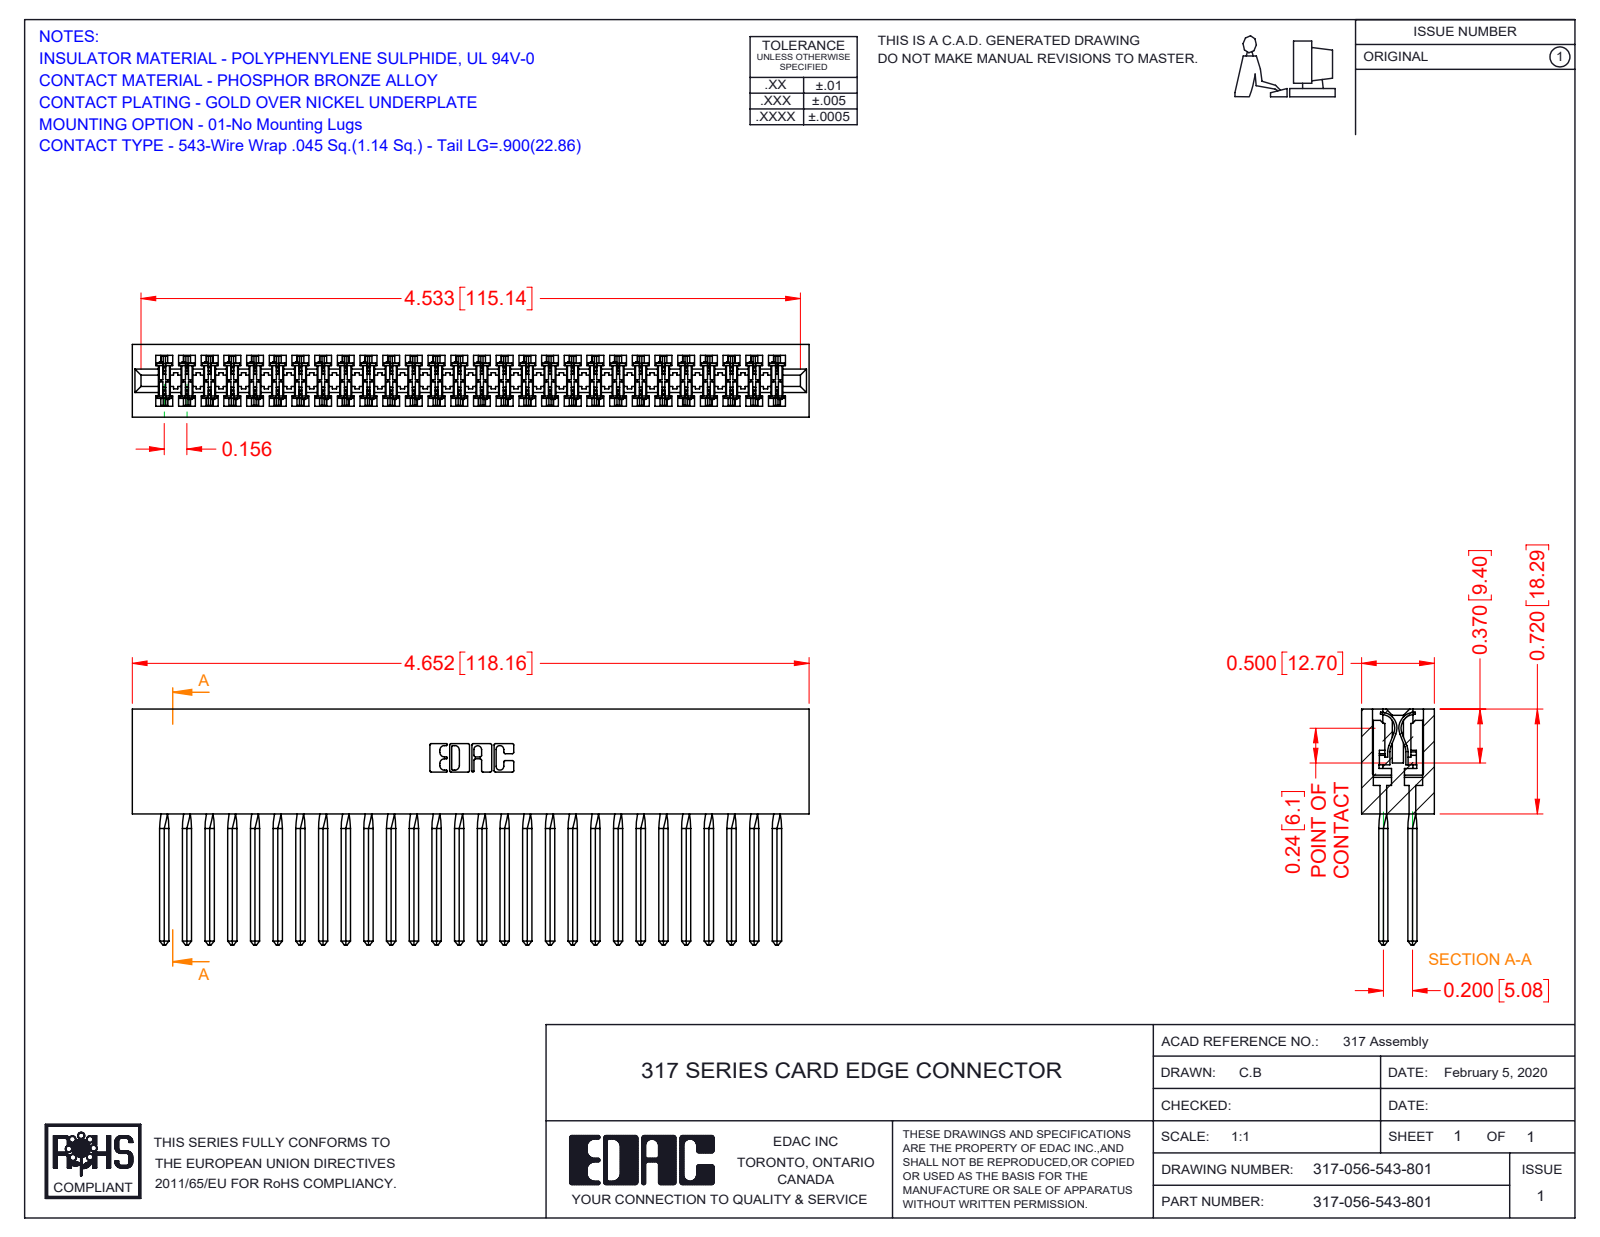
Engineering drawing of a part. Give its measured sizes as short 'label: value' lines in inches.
name: 317-056-543-801; 317 Part_Lugless; 317-290-001_543
written by: SolidWorks 2016 (CONFIG_CONTROL_DESIGN)
unit: in
bodies: 57 solids, 5074 faces (4138 planar, 712 cylindrical, 224 other)
size: 4.652 × 1.62 × 0.5
volume: 1.308 in³; area: 49.97 in²
rounds: 112× R0.015, 22× R0.01, 6× R0.007, 6× R0.031, 3× R0.026, 2× R0.095, 2× R0.1, 2× R0.11
face distances: 0.075, 0.5, 0.425, 0.35, 0.11, 0.195, 0.094, 0.2, 0.72, 0.115
